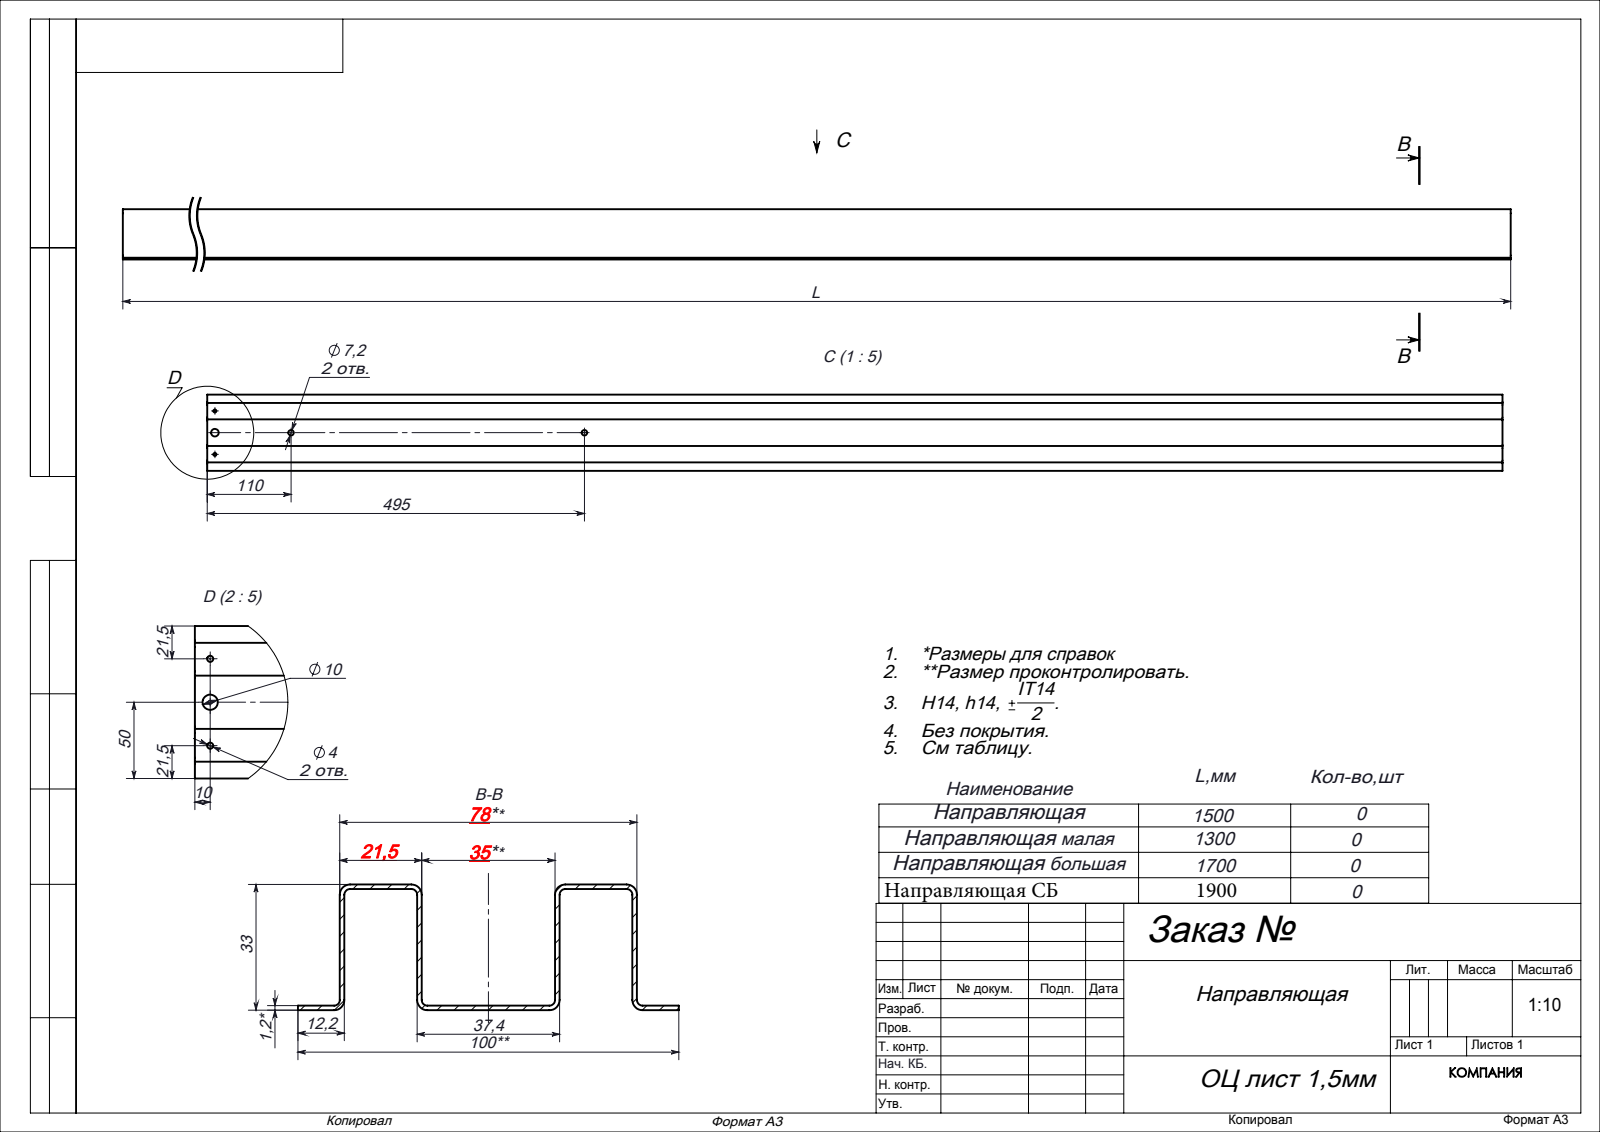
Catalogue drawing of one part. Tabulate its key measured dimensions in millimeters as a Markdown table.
| quantity | value |
| --- | --- |
| part name | Направляющая |
| STEP written by | SolidWorks 2018 (AUTOMOTIVE_DESIGN) |
| units | millimeters |
| bodies | 1 solid, 21 faces (12 planar, 9 cylindrical, 0 other) |
| overall size | 60 × 18.3 × 5.3 |
| volume | 5 253 mm³ |
| surface area | 2 982 mm² |
| round holes (diameter × count) | 3.4 × 2, 6.5 × 2 |
| partial cylindrical surfaces (radius × count) | 2.5 × 1 |
| main face-to-face distances | 5.3, 18.3, 3, 2.3, 60 |
| hole center spacings | 40 |
